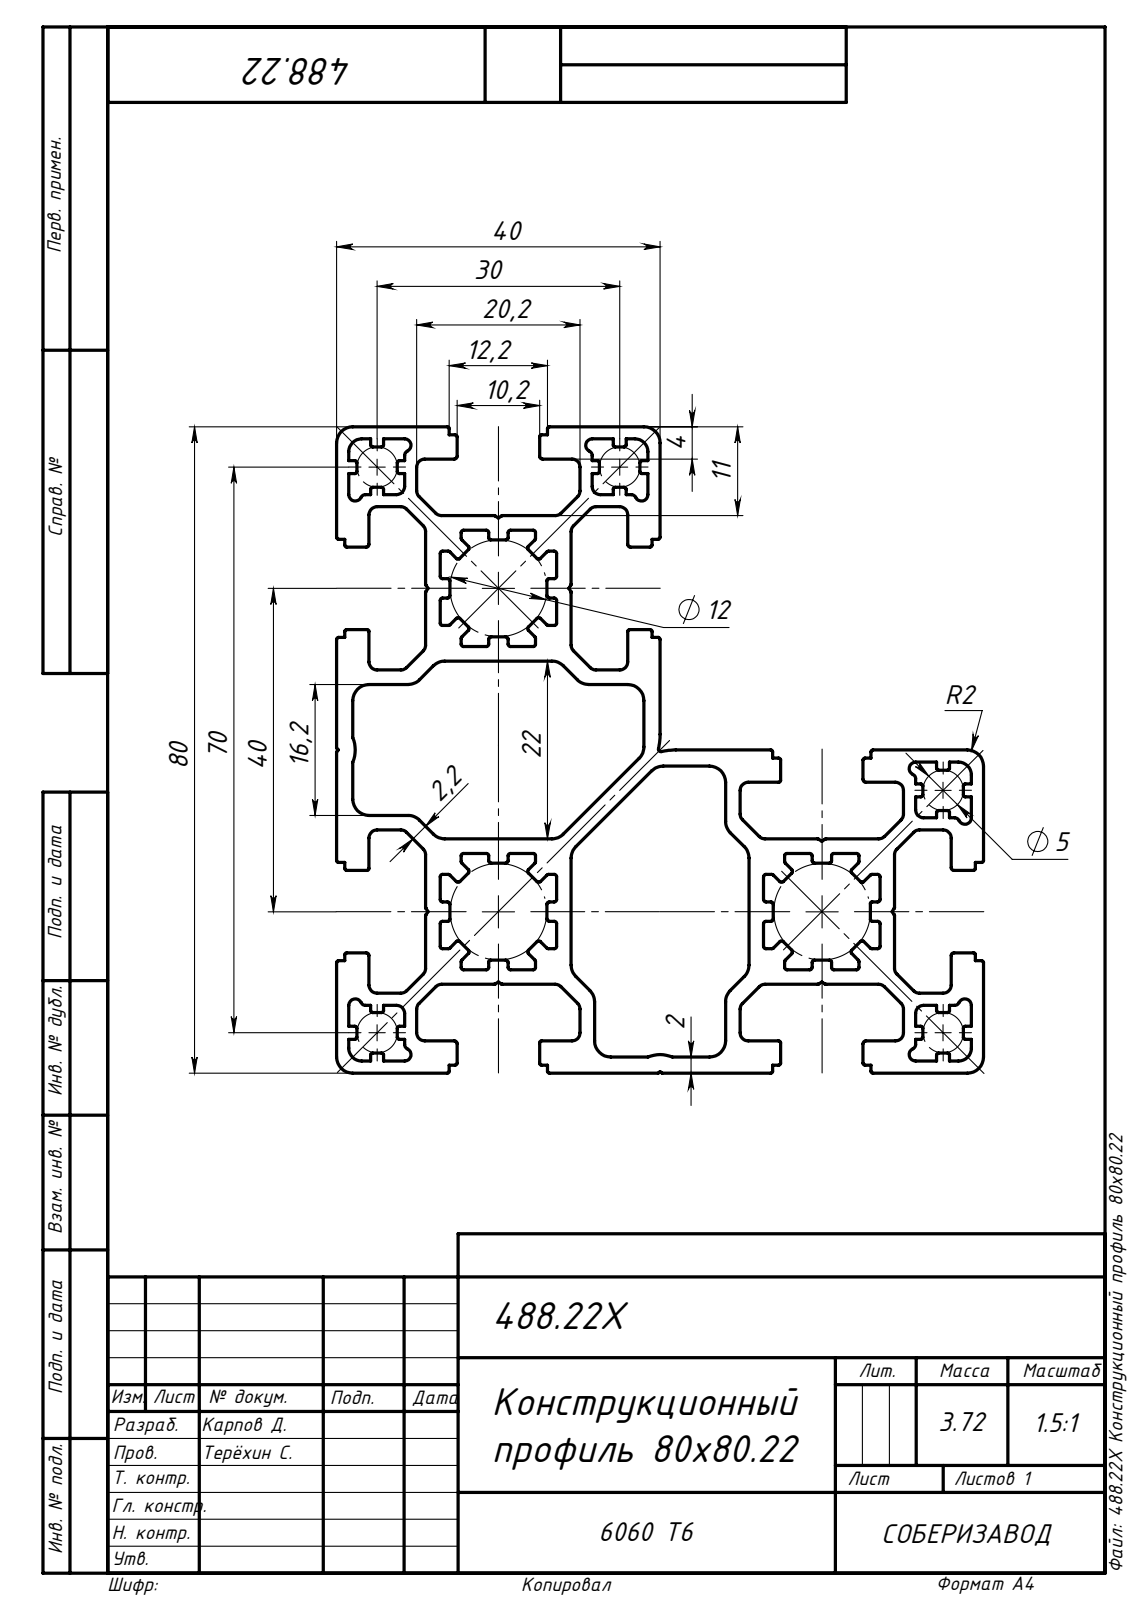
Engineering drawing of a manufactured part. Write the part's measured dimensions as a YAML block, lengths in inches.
part_name: "488.22X Конструкционный профиль 80х80.22"
step_written_by: "SolidWorks 2019 (AUTOMOTIVE_DESIGN)"
units: inches
bodies: {solids: 1, faces: 753, planar: 399, cylindrical: 354, other: 0}
overall_size: [39.37, 3.15, 3.15]
volume: 84.09
surface_area: 1877
partial_cylinders:
  - {radius: 0.01, count: 114}
  - {radius: 0.012, count: 101}
  - {radius: 0.039, count: 53}
  - {radius: 0.079, count: 27}
  - {radius: 0.014, count: 10}
  - {radius: 0.024, count: 10}
  - {radius: 0.031, count: 10}
  - {radius: 0.063, count: 5}
face_to_face_distances: [1.575, 1.142, 0.433, 0.709, 2.008, 2.717, 0.752, 0.823, 0.157, 1.417]
